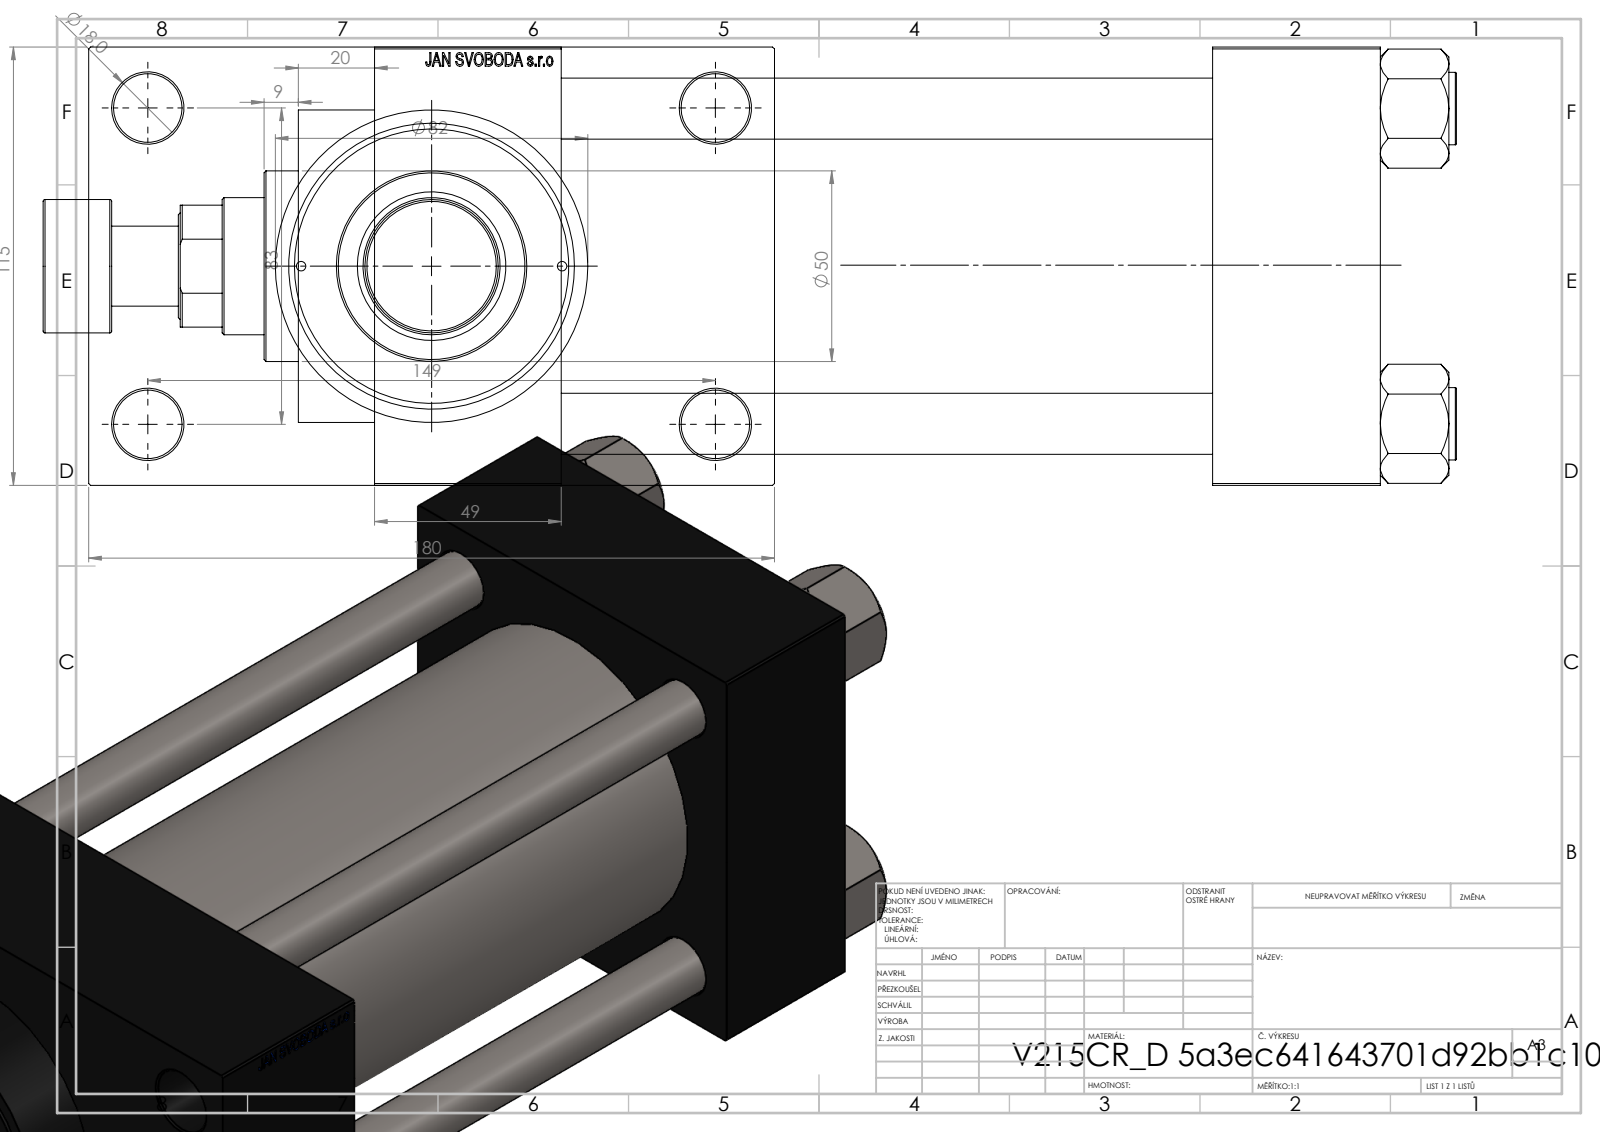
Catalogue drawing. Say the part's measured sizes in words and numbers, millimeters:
The part is named "V215CR_VCP_D; NUT_M5_D; V215_VC_A; V215CR_ROD_END_F (+2 more)". Its 3-D file was written by "SolidWorks 2019 (CONFIG_CONTROL_DESIGN)". It is 12 solids with 1173 faces: 551 planar, 96 cylindrical and 526 other. Overall it measures 371 by 180 by 115 millimeters. Its volume is 2 276 000 cubic millimeters and its surface area 389 789 square millimeters. Round holes: 4 of diameter 16, 4 of diameter 18, 2 of diameter 2.5, 2 of diameter 7, 2 of diameter 26.44, 2 of diameter 35, 1 of diameter 25.5, 1 of diameter 36, 1 of diameter 39, 1 of diameter 61, 1 of diameter 72, 1 of diameter 80. Round bosses or shafts: 4 of diameter 19, 1 of diameter 86, 1 of diameter 82, 1 of diameter 50, 1 of diameter 35, 1 of diameter 21. The main face-to-face distances are 115, 171, 49, 220, 44, 215, 264, 32.5, 147.5, 180. The hole center spacings are 33.15, 41.96, 57.81, 58.48, 82.7, 85.28, 86.17, 89.24.
